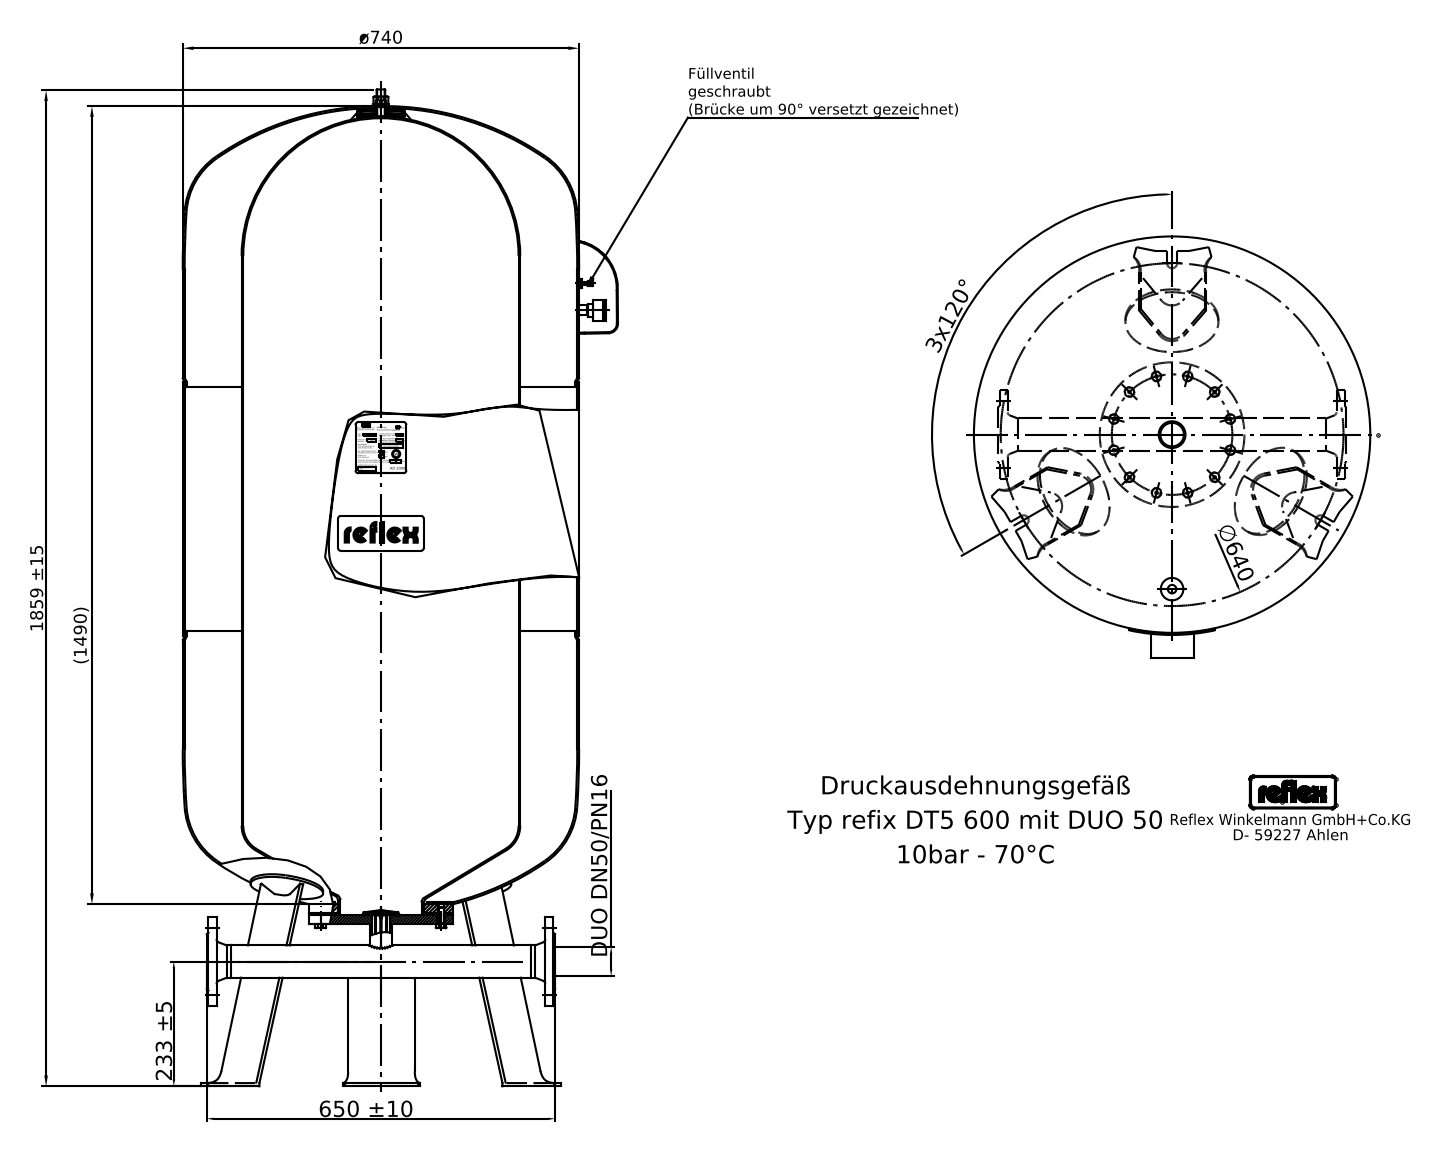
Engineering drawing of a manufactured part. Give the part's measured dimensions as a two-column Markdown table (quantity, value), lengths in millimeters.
| quantity | value |
| --- | --- |
| STEP written by | Mechanical Desktop 2008 (CONFIG_CONTROL_DESIGN) |
| units | millimeters |
| bodies | 26 solids, 522 faces (233 planar, 155 cylindrical, 134 other) |
| overall size | 1859 × 810.1 × 740 |
| volume | 596 800 000 mm³ |
| surface area | 6 722 000 mm² |
| round holes (diameter × count) | 19 × 4, 2.48 × 1, 3.8 × 1, 4.3 × 1, 4.4 × 1, 5.45 × 1, 7 × 1, 8 × 1, 11.4 × 1, 60.3 × 1, 157 × 1, 250 × 1 |
| round bosses / shafts (diameter × count) | 10 × 9, 740 × 1, 260 × 1, 230 × 1, 165 × 1, 62 × 1, 42.4 × 1, 34 × 1 |
| partial cylindrical surfaces (radius × count) | 25 × 18, 5.62 × 4, 2.25 × 3, 9 × 3, 3.84 × 2, 6.75 × 2, 8 × 2, 9.27 × 2 |
| main face-to-face distances | 1127, 6, 195, 1322, 5.97, 5.89, 201, 1328, 313, 5 |
| hole center spacings | 62.49, 88.38, 124.99, 50 |
